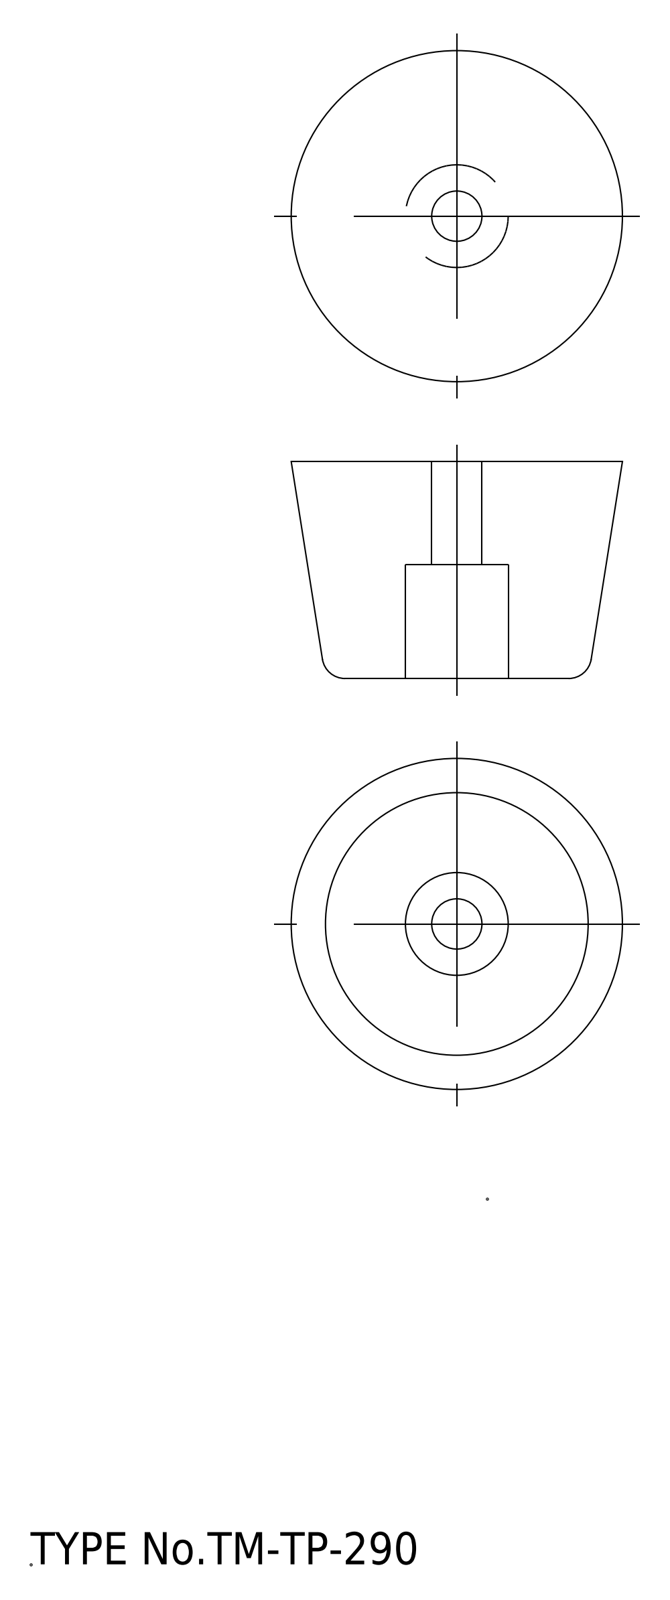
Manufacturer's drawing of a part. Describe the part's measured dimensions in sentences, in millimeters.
Its 3-D file was written by "spGate 19.8.4 (****-****-****-****) (AUTOMOTIVE_DESIGN)". It is 1 solid with 11 faces: 3 planar, 4 cylindrical and 4 other. Overall it measures 29 by 29 by 19 millimeters. Its volume is 9 337 cubic millimeters and its surface area 2 982 square millimeters. Round holes: 1 of diameter 4.4, 1 of diameter 9. The main face-to-face distances are 19, 10, 9.
